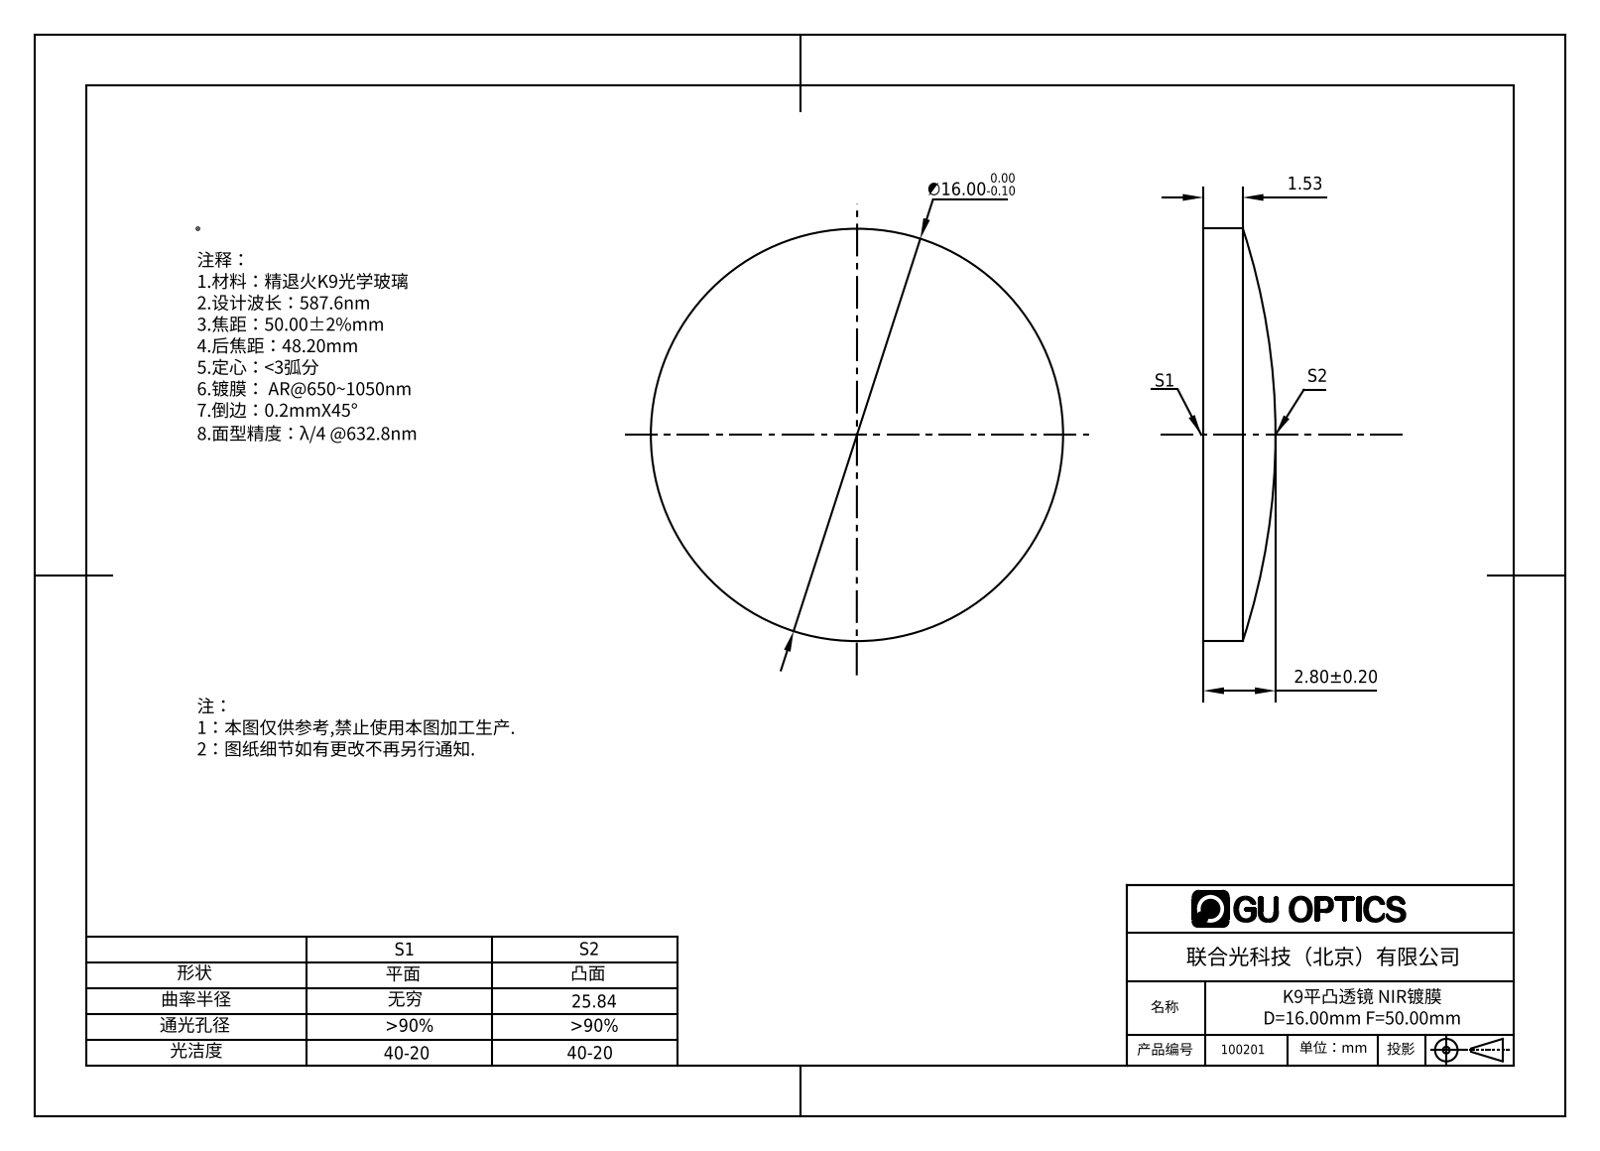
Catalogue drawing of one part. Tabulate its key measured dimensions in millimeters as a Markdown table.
| quantity | value |
| --- | --- |
| part name | 100201 |
| STEP written by | SolidWorks 2016 (AUTOMOTIVE_DESIGN) |
| units | millimeters |
| bodies | 1 solid, 5 faces (1 planar, 2 cylindrical, 2 other) |
| overall size | 16 × 16 × 2.8 |
| volume | 436 mm³ |
| surface area | 484 mm² |
| round bosses / shafts (diameter × count) | 16 × 1 |
